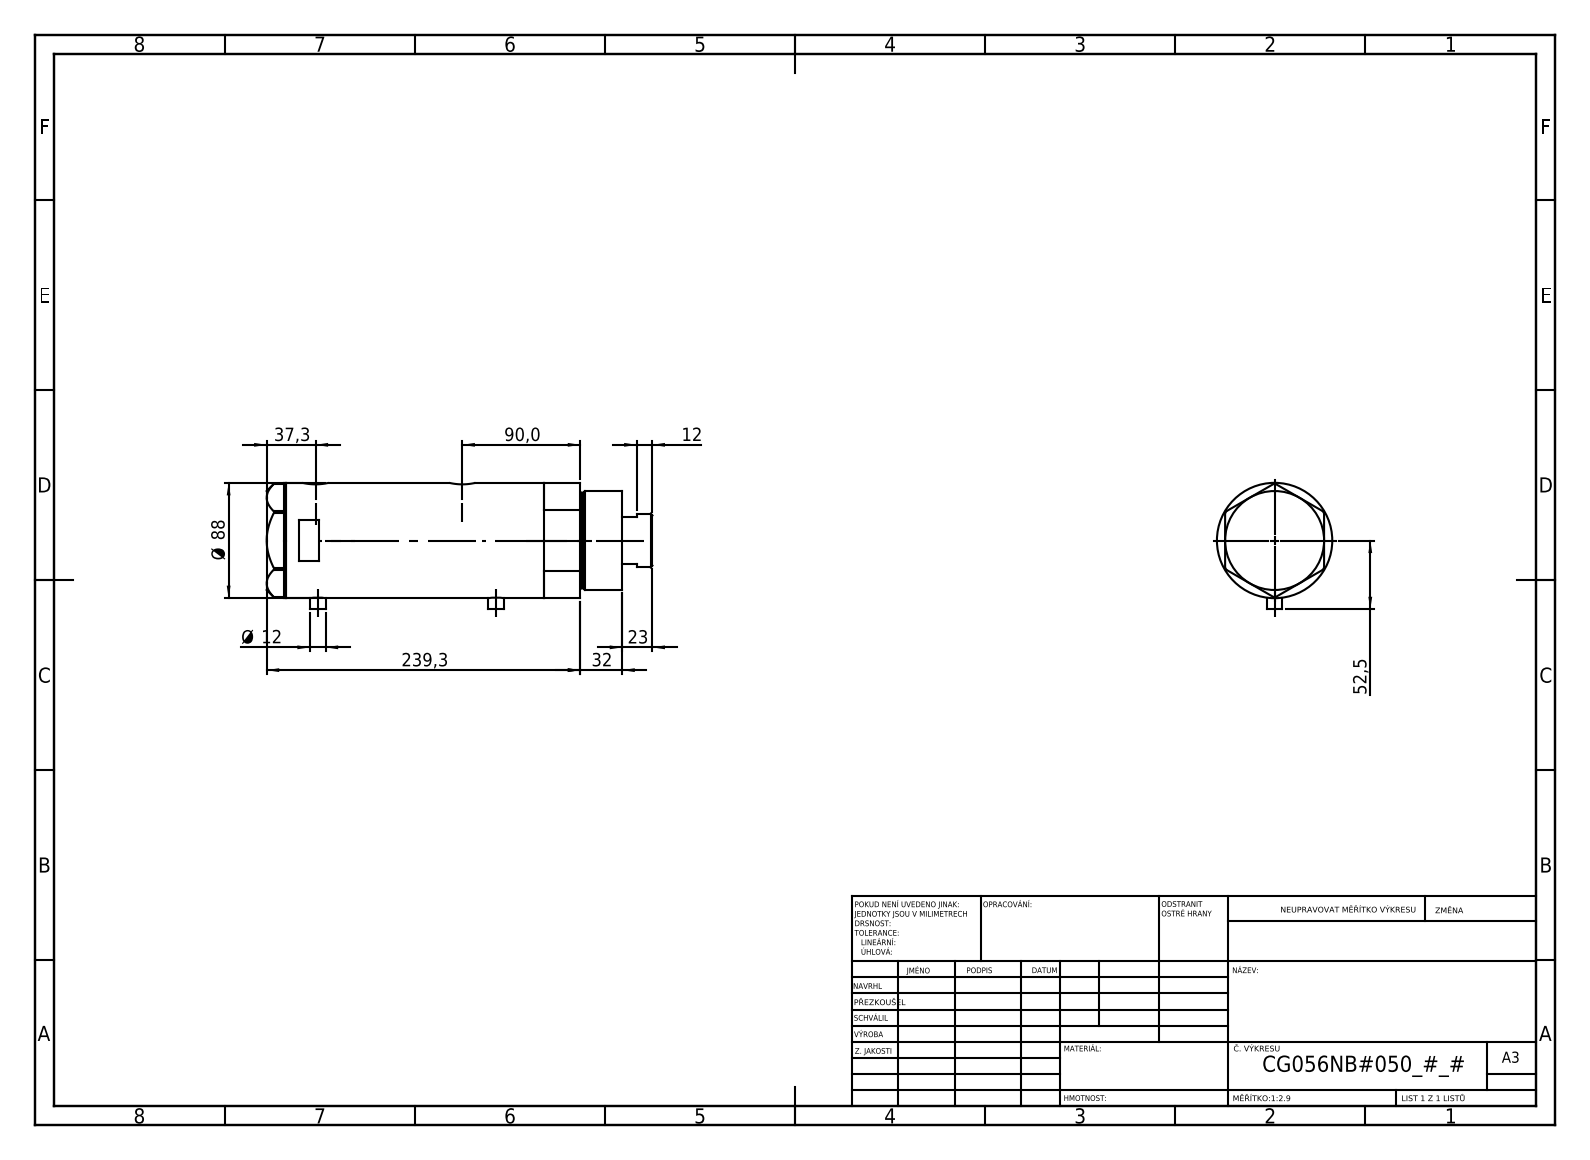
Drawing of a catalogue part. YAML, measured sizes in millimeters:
part_name: "V270CG_VC; V270CG_MIDDLE; V270CG_BACK; V270CG_FRONT"
step_written_by: "SolidWorks 2019 (CONFIG_CONTROL_DESIGN)"
units: millimeters
bodies: {solids: 4, faces: 121, planar: 52, cylindrical: 49, other: 20}
overall_size: [294.3, 96.5, 88]
volume: 1534000
surface_area: 221434
round_holes:
  - {diameter: 12.5, count: 2}
  - {diameter: 13.16, count: 2}
  - {diameter: 20, count: 2}
  - {diameter: 14.5, count: 1}
  - {diameter: 42, count: 1}
  - {diameter: 43.5, count: 1}
  - {diameter: 56, count: 1}
  - {diameter: 60, count: 1}
  - {diameter: 80, count: 1}
round_bosses_or_shafts:
  - {diameter: 12, count: 2}
  - {diameter: 88, count: 1}
  - {diameter: 75, count: 1}
  - {diameter: 73, count: 1}
  - {diameter: 41, count: 1}
face_to_face_distances: [134.4, 26, 108.4, 15, 41, 149.4, 256.3, 271.3, 230.3, 121.9]
hole_center_spacings: [1.7, 25.8, 110.3, 112, 136.1, 137.8]
